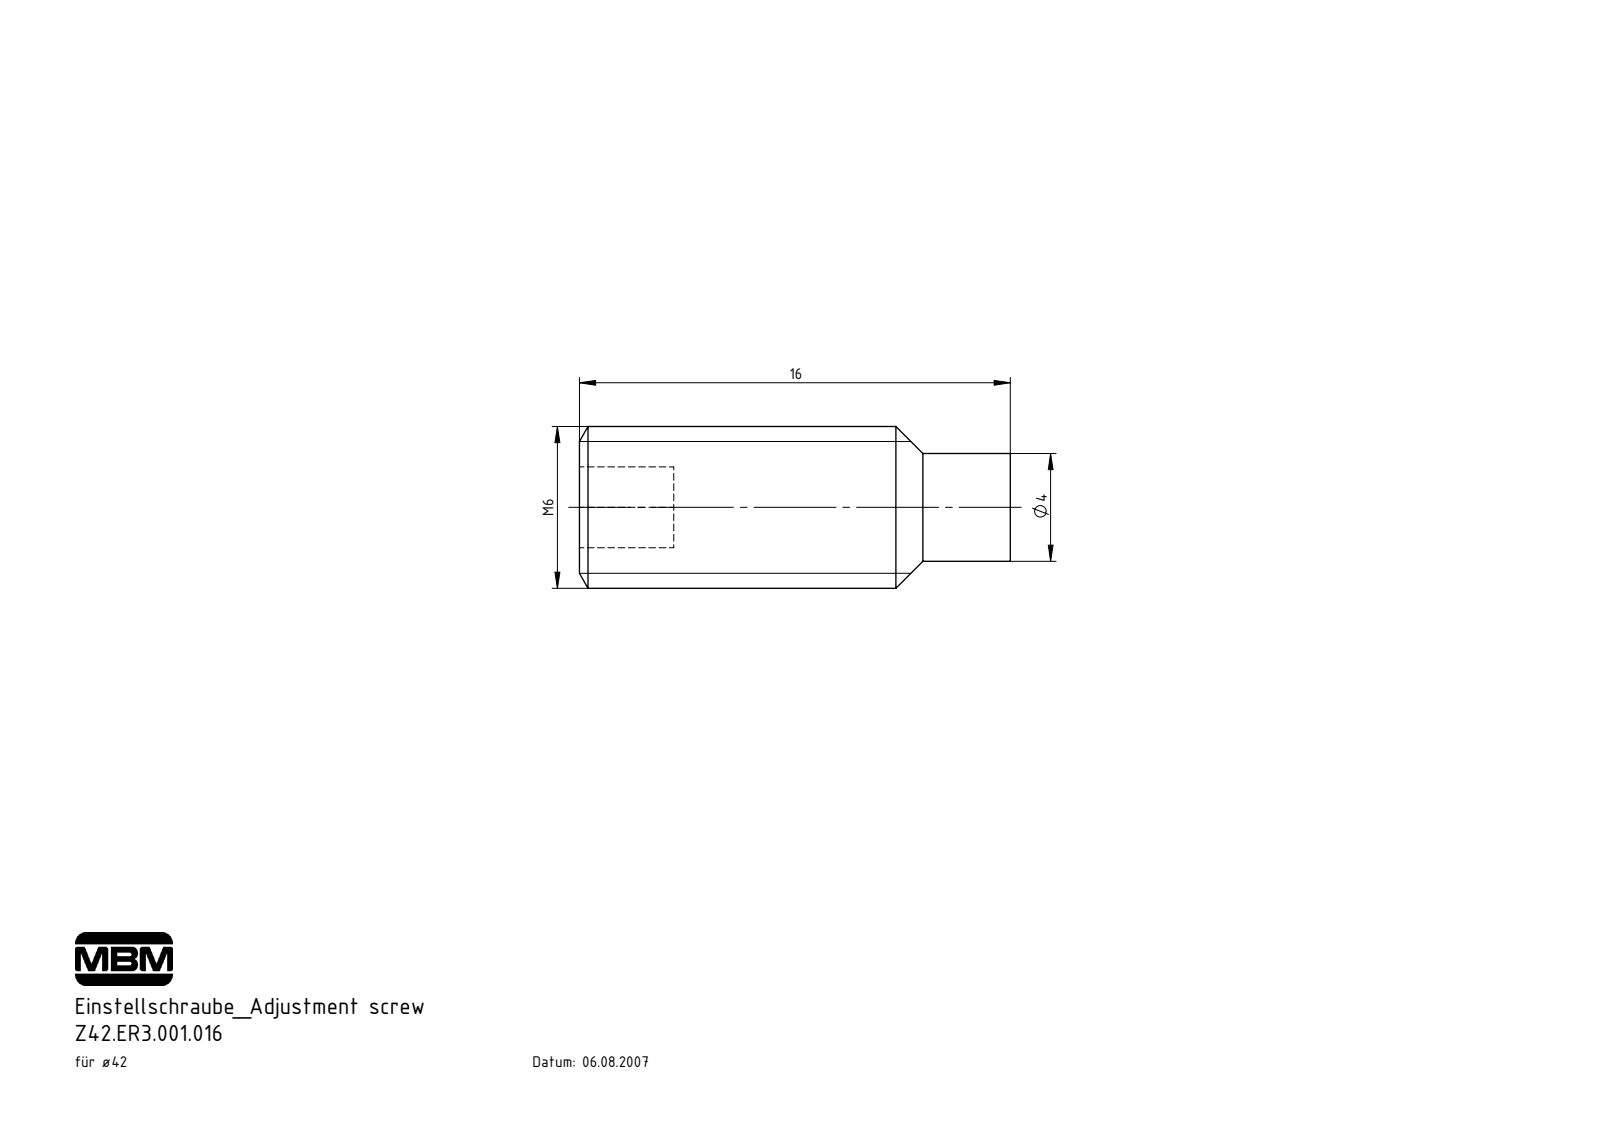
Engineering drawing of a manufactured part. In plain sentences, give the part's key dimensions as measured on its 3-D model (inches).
The part is named "Z42.ER3.001.016". Its 3-D file was written by "SolidWorks 2017 (AUTOMOTIVE_DESIGN)". It is 1 solid with 17 faces: 9 planar, 4 cylindrical and 4 other. Overall it measures 0.63 by 0.236 by 0.236 inches. Its volume is 0.022 cubic inches and its surface area 0.553 square inches. Round bosses or shafts: 1 of diameter 0.236, 1 of diameter 0.157. The main face-to-face distances are 0.118, 0.63, 0.138, 0.492.
